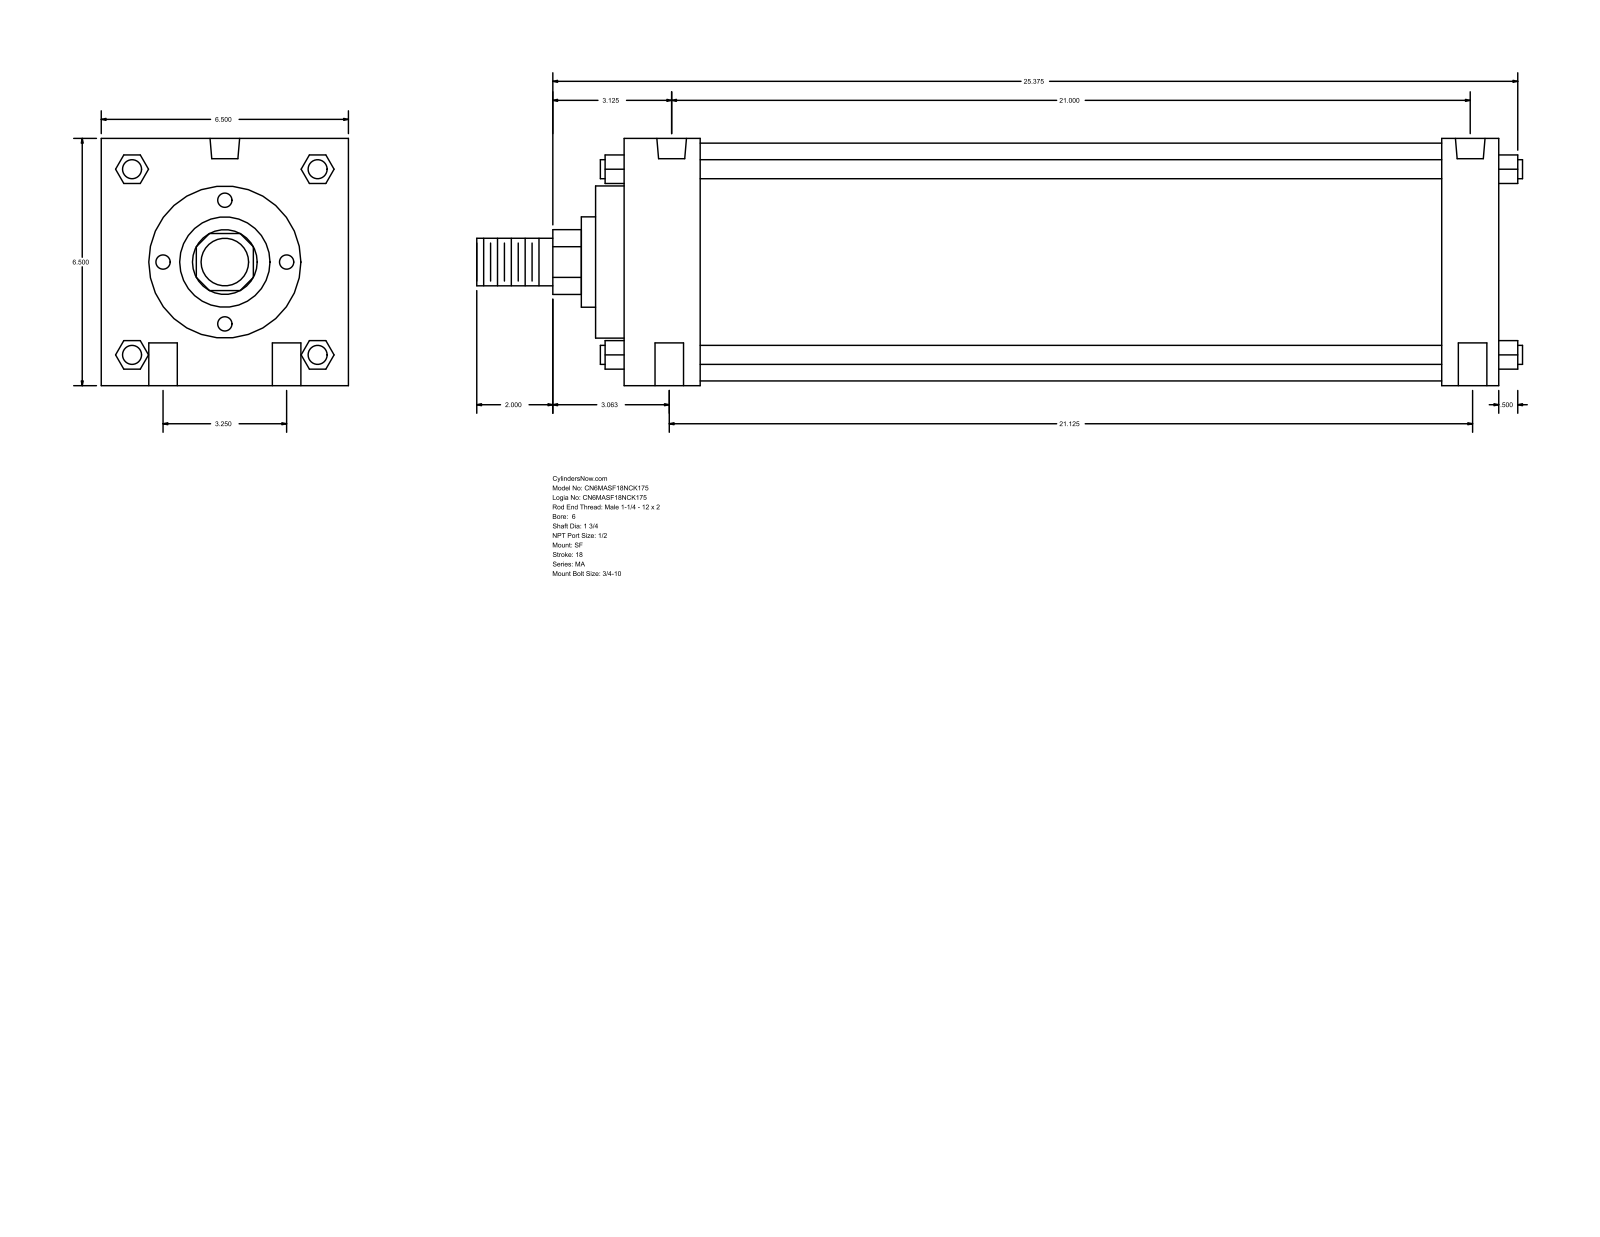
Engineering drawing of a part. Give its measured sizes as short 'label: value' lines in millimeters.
name: MA_SF__0600_1.75
written by: GSSL Pune (CONFIG_CONTROL_DESIGN)
unit: mm
bodies: 0 solids, 126 faces (95 planar, 31 cylindrical, 0 other)
size: 698.5 × 165.1 × 165.1
holes: 4× ⌀19.05, 2× ⌀17.46, 2× ⌀19.77
bosses: 4× ⌀12.7, 1× ⌀158.75, 1× ⌀101.6, 1× ⌀60.33, 1× ⌀44.45, 1× ⌀31.75
rounds: 1× R21.63
face distances: 165.1, 584.21, 19.05, 50.8, 38.1, 546.11, 495.31, 533.41, 69.85, 565.16
hole spacings: 536.57, 41.3, 82.54, 533.39, 542.88
